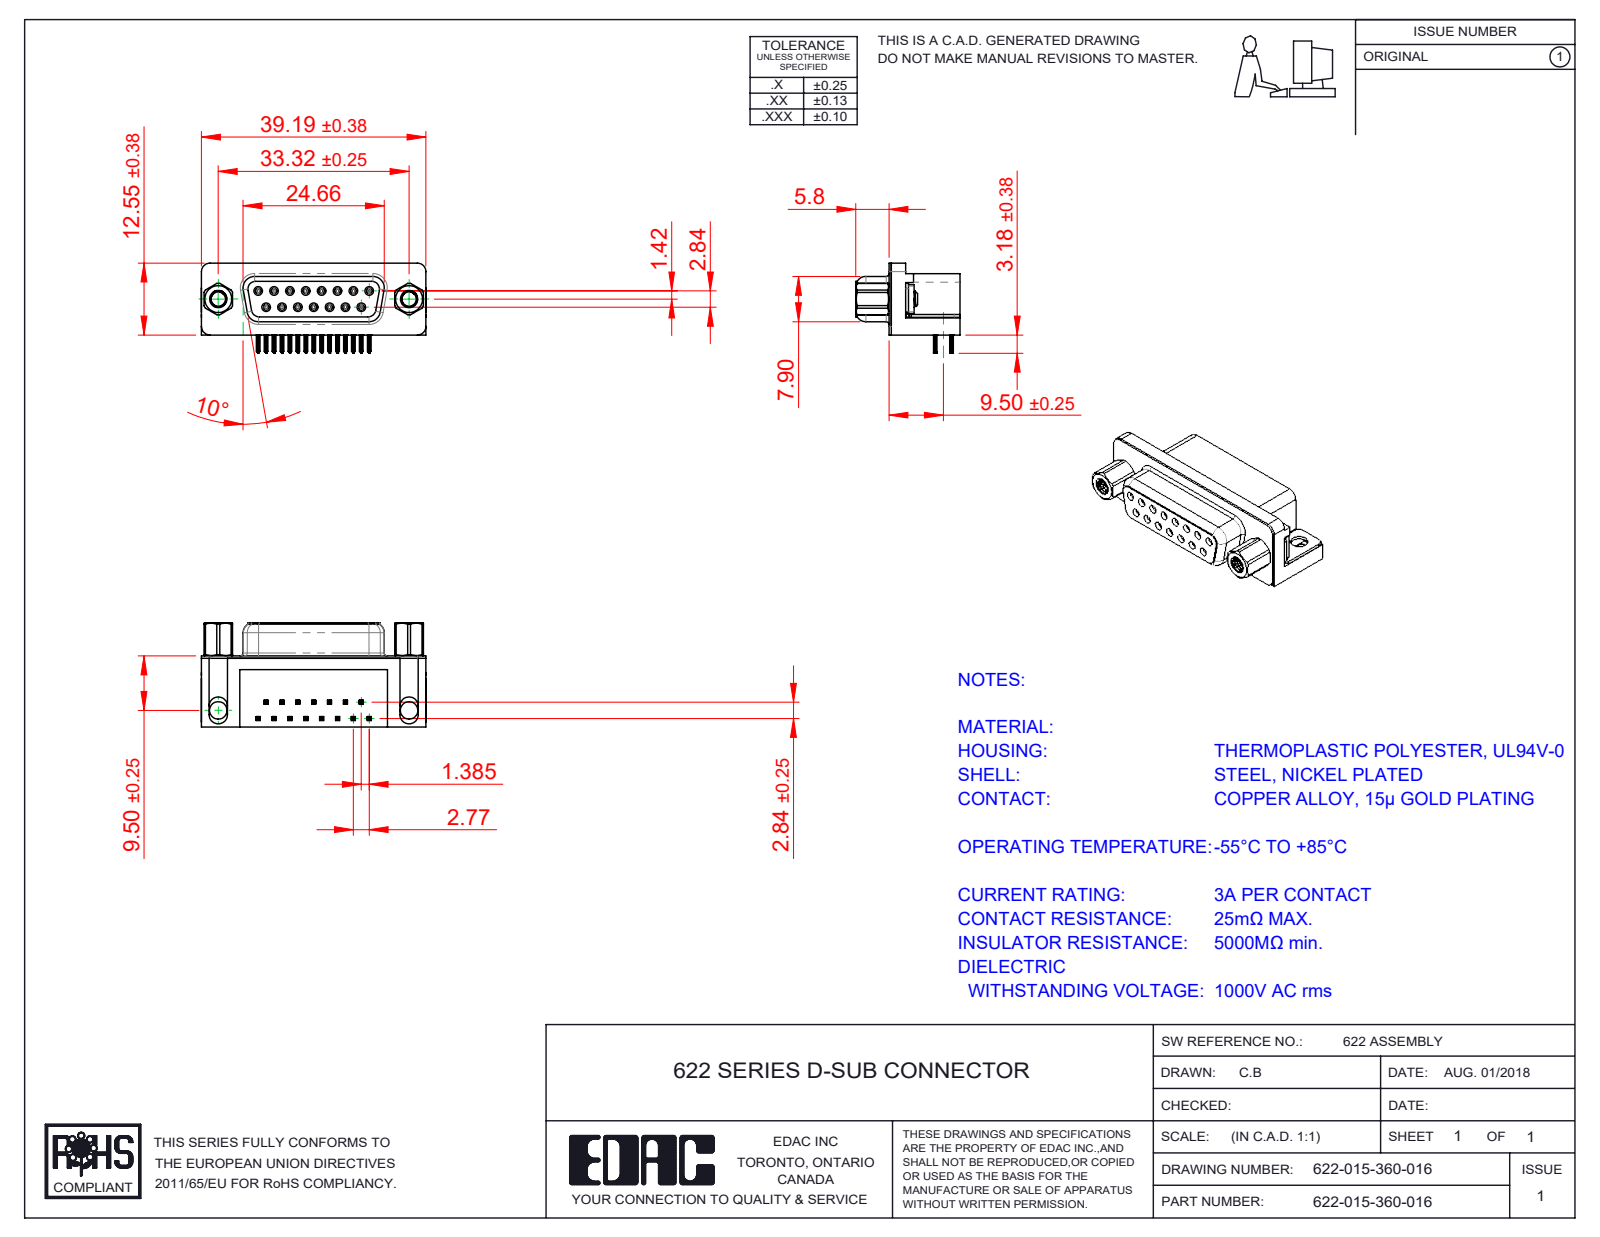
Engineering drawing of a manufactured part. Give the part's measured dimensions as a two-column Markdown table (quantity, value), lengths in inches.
| quantity | value |
| --- | --- |
| part name | 622-015-360-016; 622 M3 Threaded Rivet; 622 Socket Bottom; 622 Housing_15 Socket (+3 more) |
| STEP written by | SolidWorks 2016 (CONFIG_CONTROL_DESIGN) |
| units | inches |
| bodies | 21 solids, 2425 faces (1072 planar, 609 cylindrical, 744 other) |
| overall size | 1.544 × 0.717 × 0.619 |
| volume | 0.316 in³ |
| surface area | 10.39 in² |
| round holes (diameter × count) | 0.031 × 15, 0.035 × 15, 0.098 × 2, 0.12 × 2, 0.157 × 2, 0.189 × 2, 0.197 × 2 |
| round bosses / shafts (diameter × count) | 0.047 × 15, 0.193 × 2, 0.187 × 2, 0.154 × 2 |
| partial cylindrical surfaces (radius × count) | 0.004 × 120, 0.006 × 60, 0.014 × 30, 0.039 × 18, 0.013 × 15, 0.01 × 8, 0.053 × 8, 0.059 × 8 |
| main face-to-face distances | 0.016, 0.472, 0.244, 0.488, 0.407, 0.114, 0.262, 0.033, 0.014, 0.228 |
| hole center spacings | 0.124, 0.109, 0.218, 0.327, 0.436, 0.198, 0.198, 0.294 |
